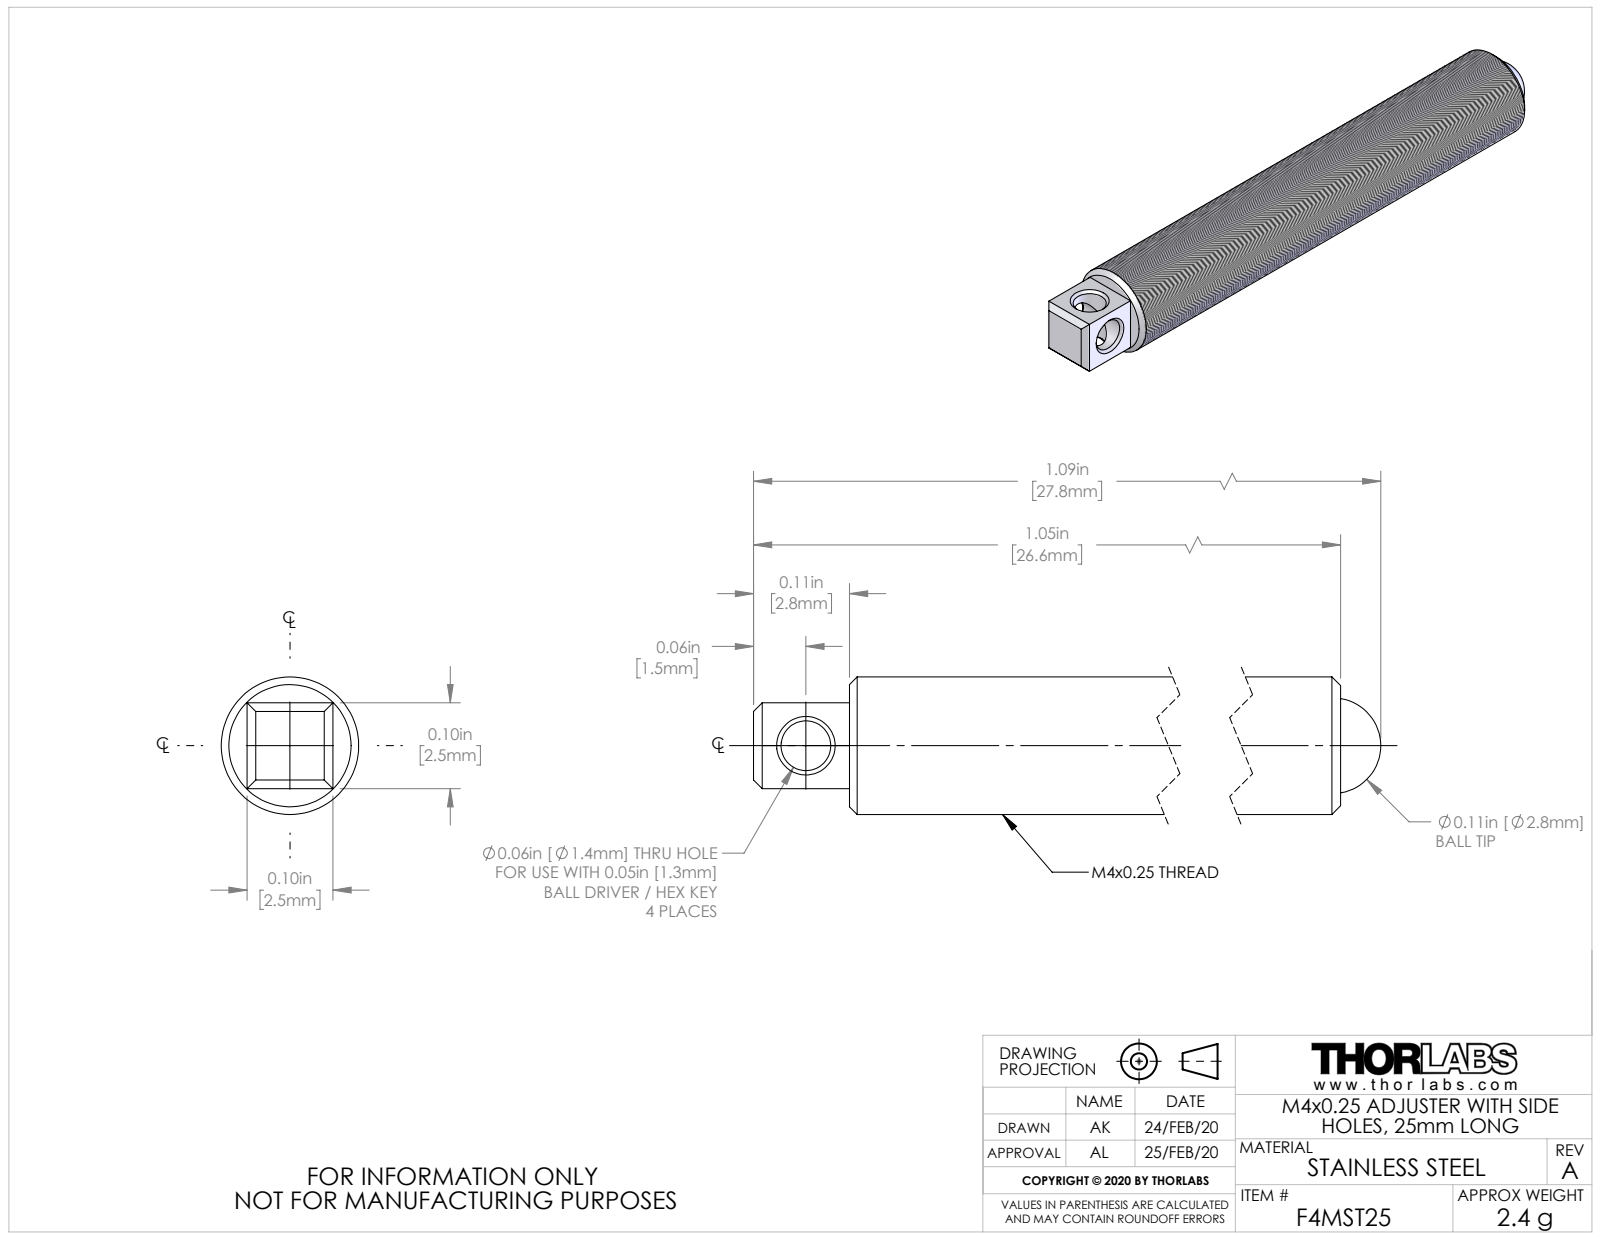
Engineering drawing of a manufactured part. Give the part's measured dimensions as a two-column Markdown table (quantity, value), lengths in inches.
| quantity | value |
| --- | --- |
| part name | TTN203605-E0W |
| STEP written by | SolidWorks 2018 (AUTOMOTIVE_DESIGN) |
| units | inches |
| bodies | 2 solids, 41 faces (11 planar, 12 cylindrical, 18 other) |
| overall size | 1.094 × 0.157 × 0.157 |
| volume | 0.019 in³ |
| surface area | 0.601 in² |
| round holes (diameter × count) | 0.057 × 2, 0.11 × 1 |
| round bosses / shafts (diameter × count) | 0.157 × 1 |
| main face-to-face distances | 0.098, 0.11, 0.939, 1.048 |
